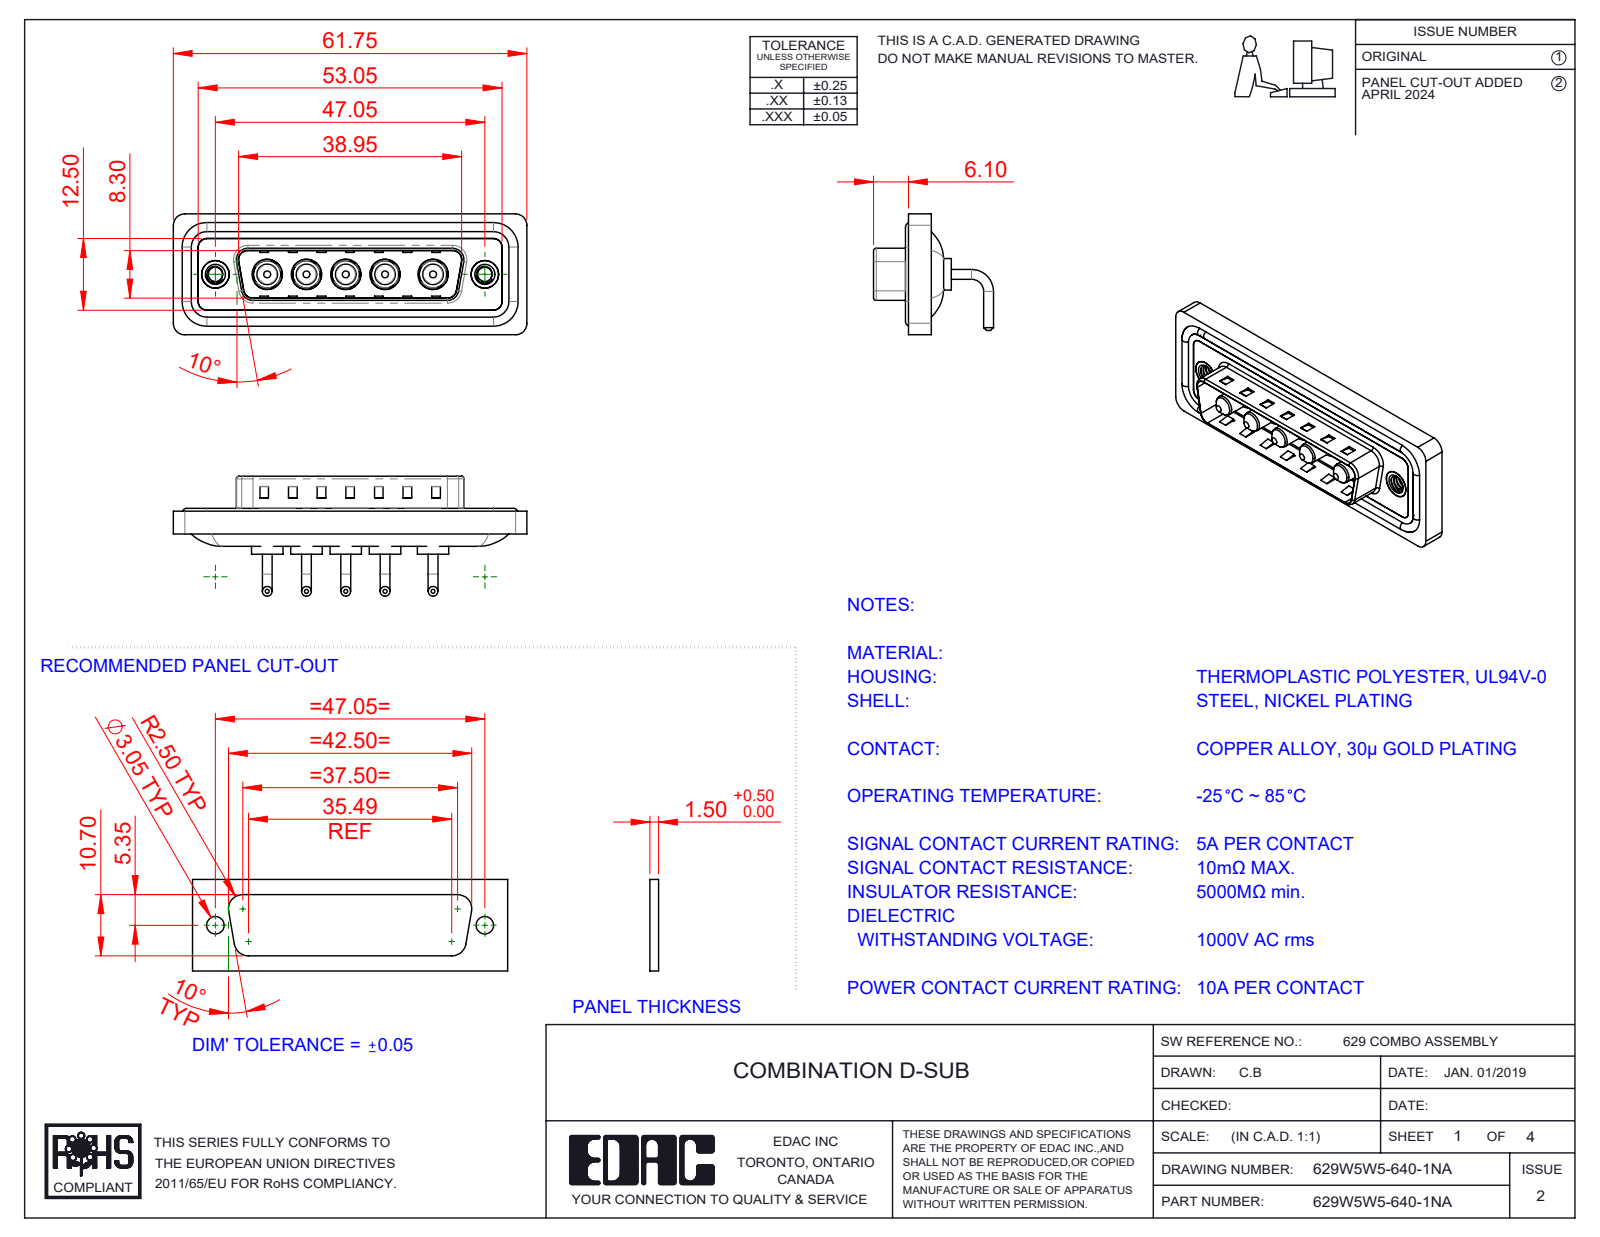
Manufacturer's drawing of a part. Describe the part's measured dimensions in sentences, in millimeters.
The part is named "Power Pin_10A RA; 629Combo Shell Front_25 Contacts; 629Combo Waterproof Housing_25 Contacts; 629Combo Housing_5W5 (+3 more)". Its 3-D file was written by "SolidWorks 2023 (CONFIG_CONTROL_DESIGN)". It is 17 solids with 692 faces: 259 planar, 291 cylindrical and 142 other. Overall it measures 61.75 by 21.1 by 20.95 millimeters. Its volume is 7 516 cubic millimeters and its surface area 12 021 square millimeters. Round holes: 5 of diameter 4.85, 5 of diameter 5.3, 2 of diameter 2.5, 2 of diameter 4, 2 of diameter 4.8, 2 of diameter 5. Round bosses or shafts: 10 of diameter 1.7, 5 of diameter 5.5, 5 of diameter 5.2, 5 of diameter 4.75, 5 of diameter 3.75, 5 of diameter 3.6, 4 of diameter 1.6, 2 of diameter 4.9. Partial cylindrical surfaces (rounded edges, fillets, slot ends): 18 of radius 1.5, 18 of radius 2, 8 of radius 0.5, 8 of radius 1.6, 5 of radius 2.1, 4 of radius 0.25, 4 of radius 0.6, 4 of radius 0.65. The main face-to-face distances are 0.4, 2.9, 0.8, 4.5, 4.1, 1.5, 1.1, 2.1, 3.1, 6. The hole center spacings are 6.86, 13.73, 6.85, 6.87, 8.37, 8.38, 9.04, 9.05.
